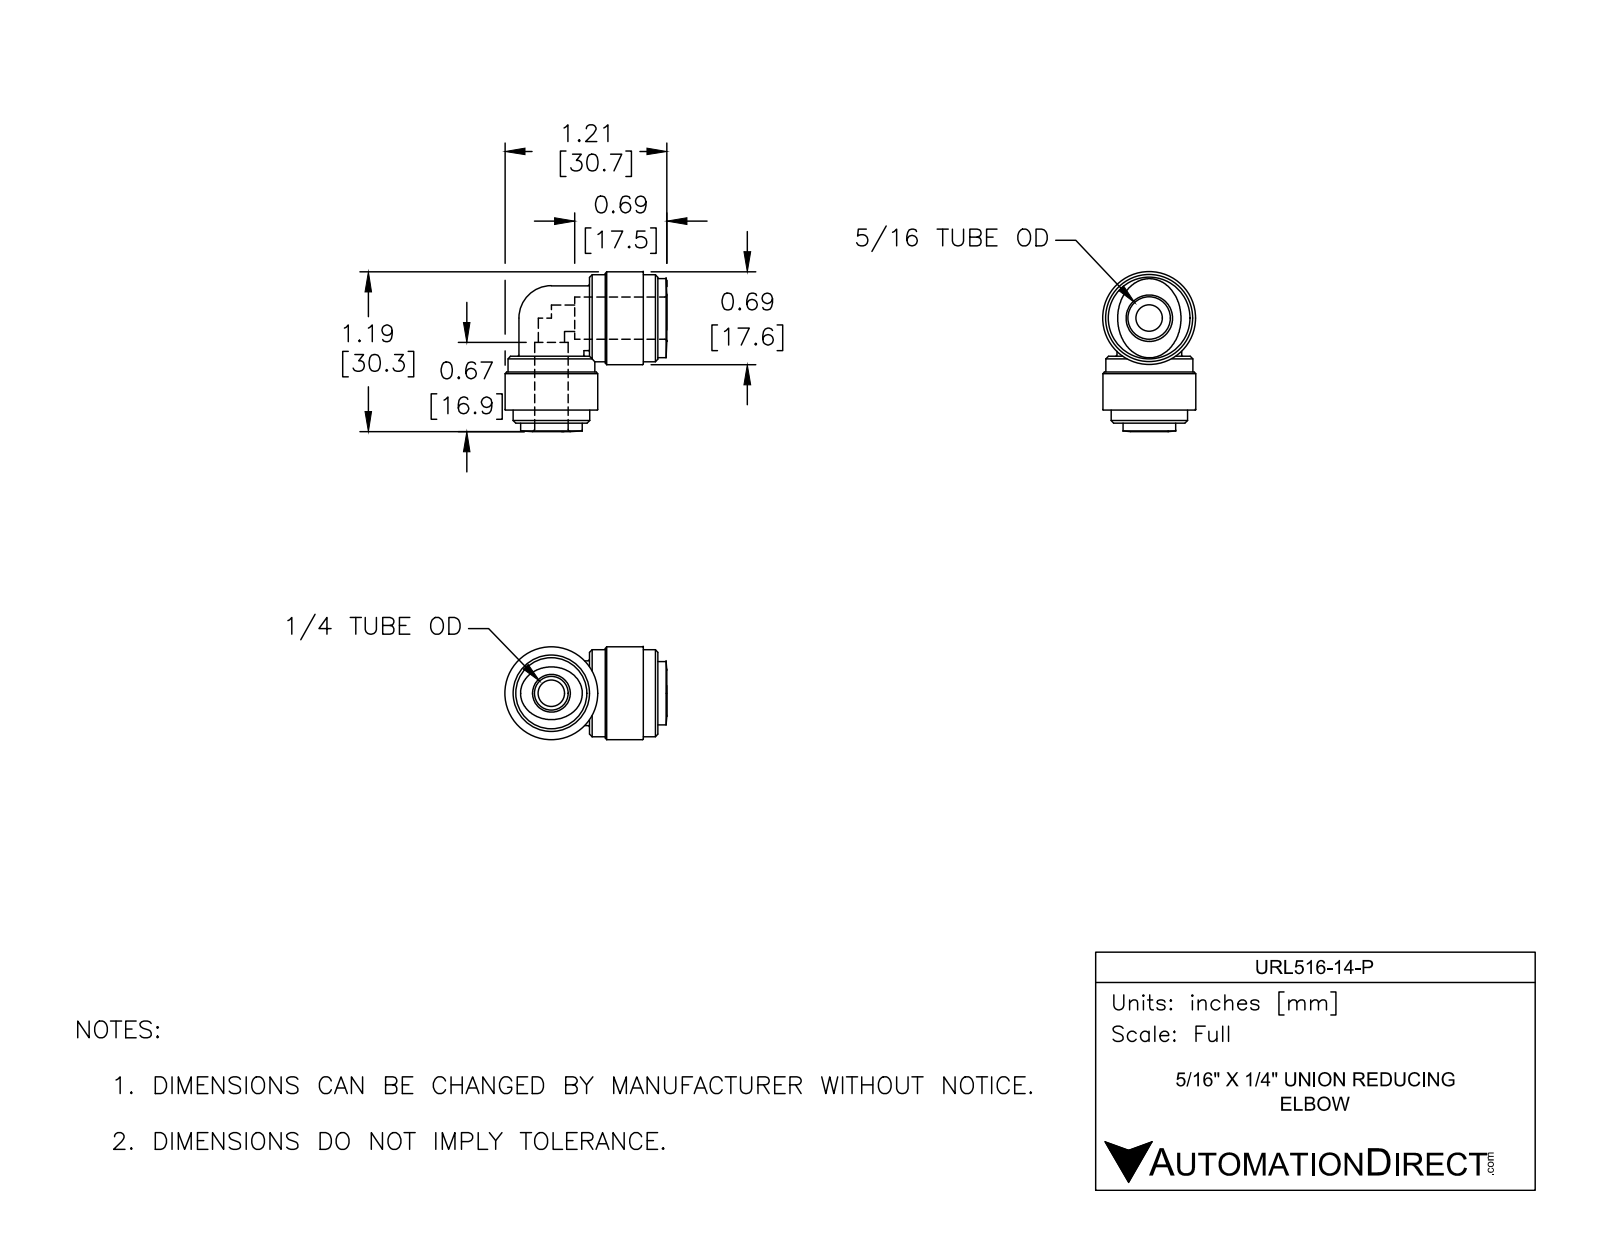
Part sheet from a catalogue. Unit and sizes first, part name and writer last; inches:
Units: inches
Overall size (bounding box): 1.209 × 1.193 × 0.693
Round holes (diameter × count): ⌀0.197 ×2, ⌀0.25 ×1, ⌀0.315 ×1
Round bosses / shafts (diameter × count): ⌀0.693 ×2, ⌀0.65 ×2, ⌀0.484 ×2, ⌀0.571 ×1
Main face-to-face distances: 0.402, 0.512, 0.11, 0.098, 0.5, 0.622, 0.118, 0.283, 0.228, 0.394
Volume: 0.378 in³ · Surface area: 5.426 in²
Bodies: 1 solid, 67 faces (10 planar, 24 cylindrical, 33 other)
Part name (STEP PRODUCT): URL516-14-P
STEP written by: SolidWorks 2017 (AUTOMOTIVE_DESIGN)
